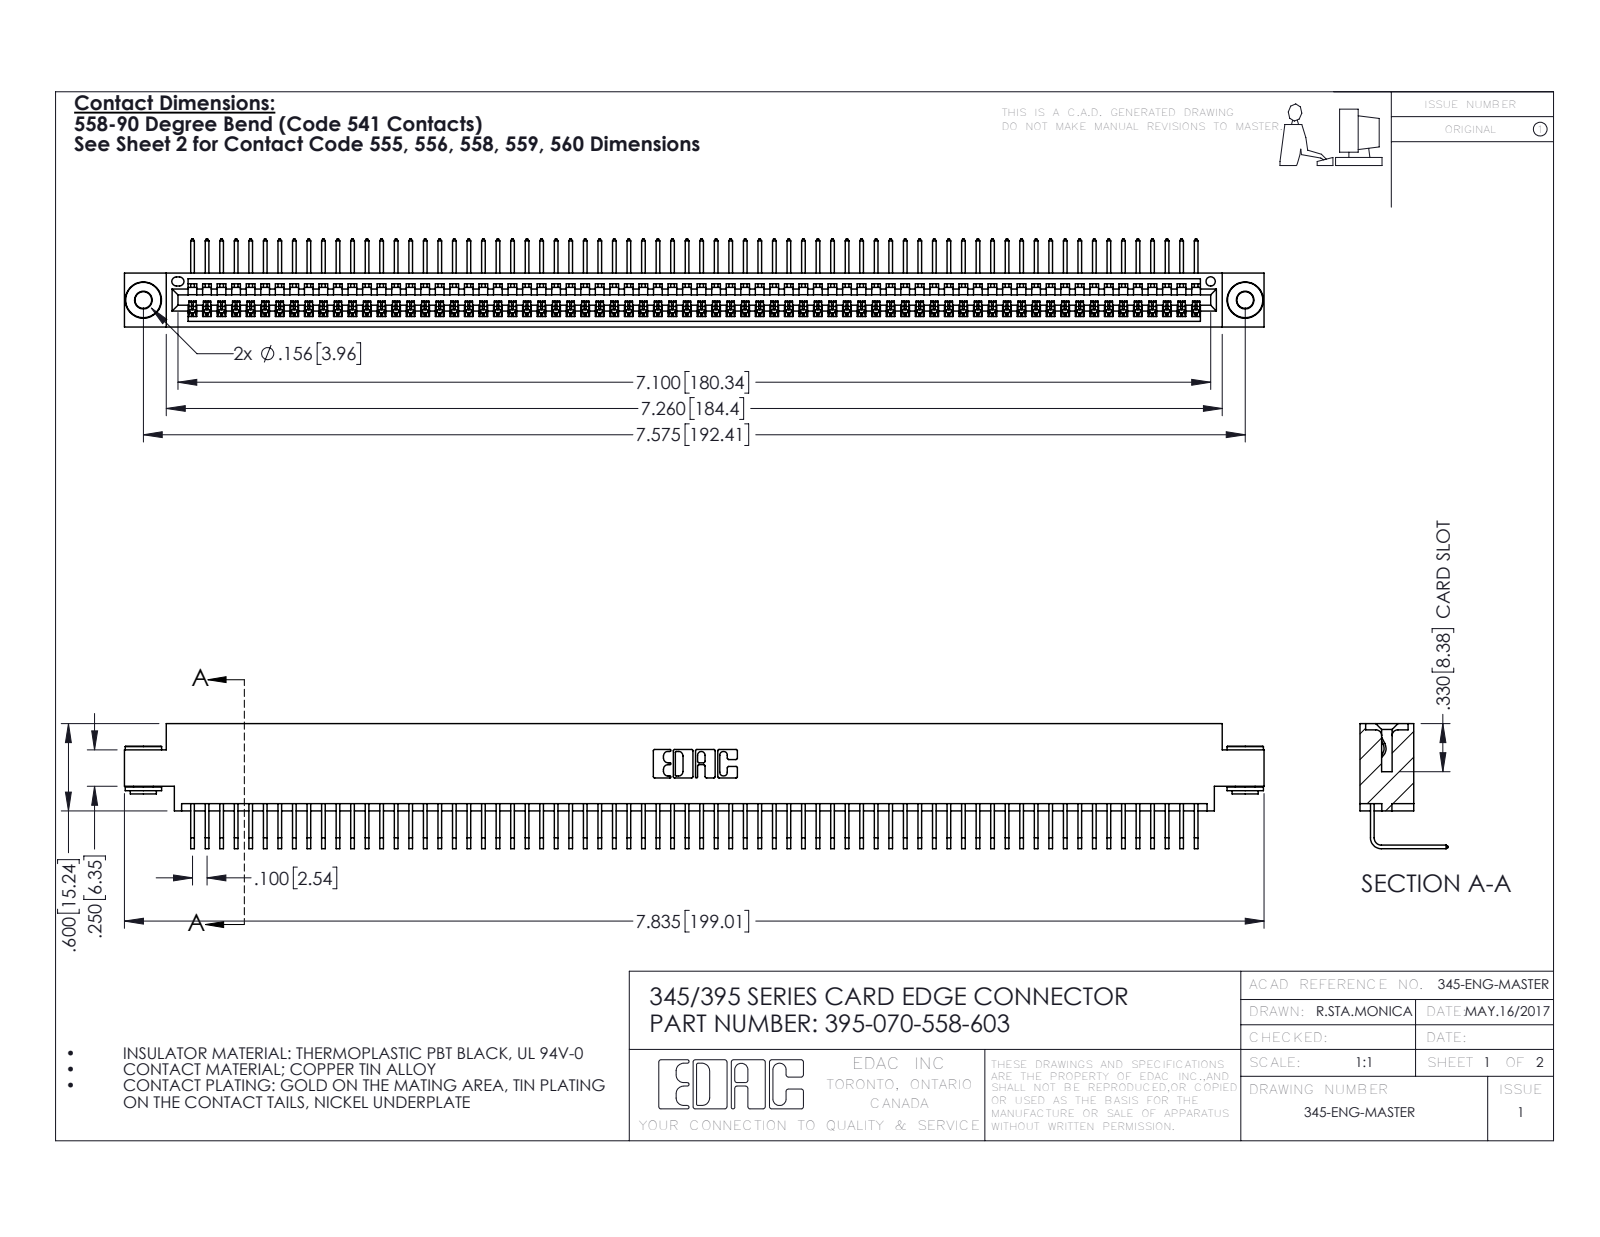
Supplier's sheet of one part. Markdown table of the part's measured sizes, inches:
| quantity | value |
| --- | --- |
| part name | 345-250-002_345-250-002-102; 395-070-558-603; 345 Part_0.170 Offset - 0.156 Dia-TH; 345-292-001_558 Tail - 2 |
| STEP written by | SolidWorks 2016 (CONFIG_CONTROL_DESIGN) |
| units | inches |
| bodies | 73 solids, 4368 faces (3034 planar, 1326 cylindrical, 8 other) |
| overall size | 7.835 × 0.859 × 0.605 |
| volume | 1.176 in³ |
| surface area | 42.94 in² |
| round holes (diameter × count) | 0.116 × 2, 0.156 × 2, 0.064 × 1 |
| round bosses / shafts (diameter × count) | 0.25 × 2, 0.18 × 2, 0.136 × 2 |
| partial cylindrical surfaces (radius × count) | 0.006 × 140, 0.01 × 22, 0.007 × 6, 0.031 × 6, 0.026 × 3, 0.031 × 2, 0.04 × 2, 0.014 × 1 |
| main face-to-face distances | 0.072, 0.298, 0.37, 0.2, 0.098, 0.272, 0.025, 0.225, 0.175, 0.149 |
| hole center spacings | 0.27, 7.339, 7.575 |
